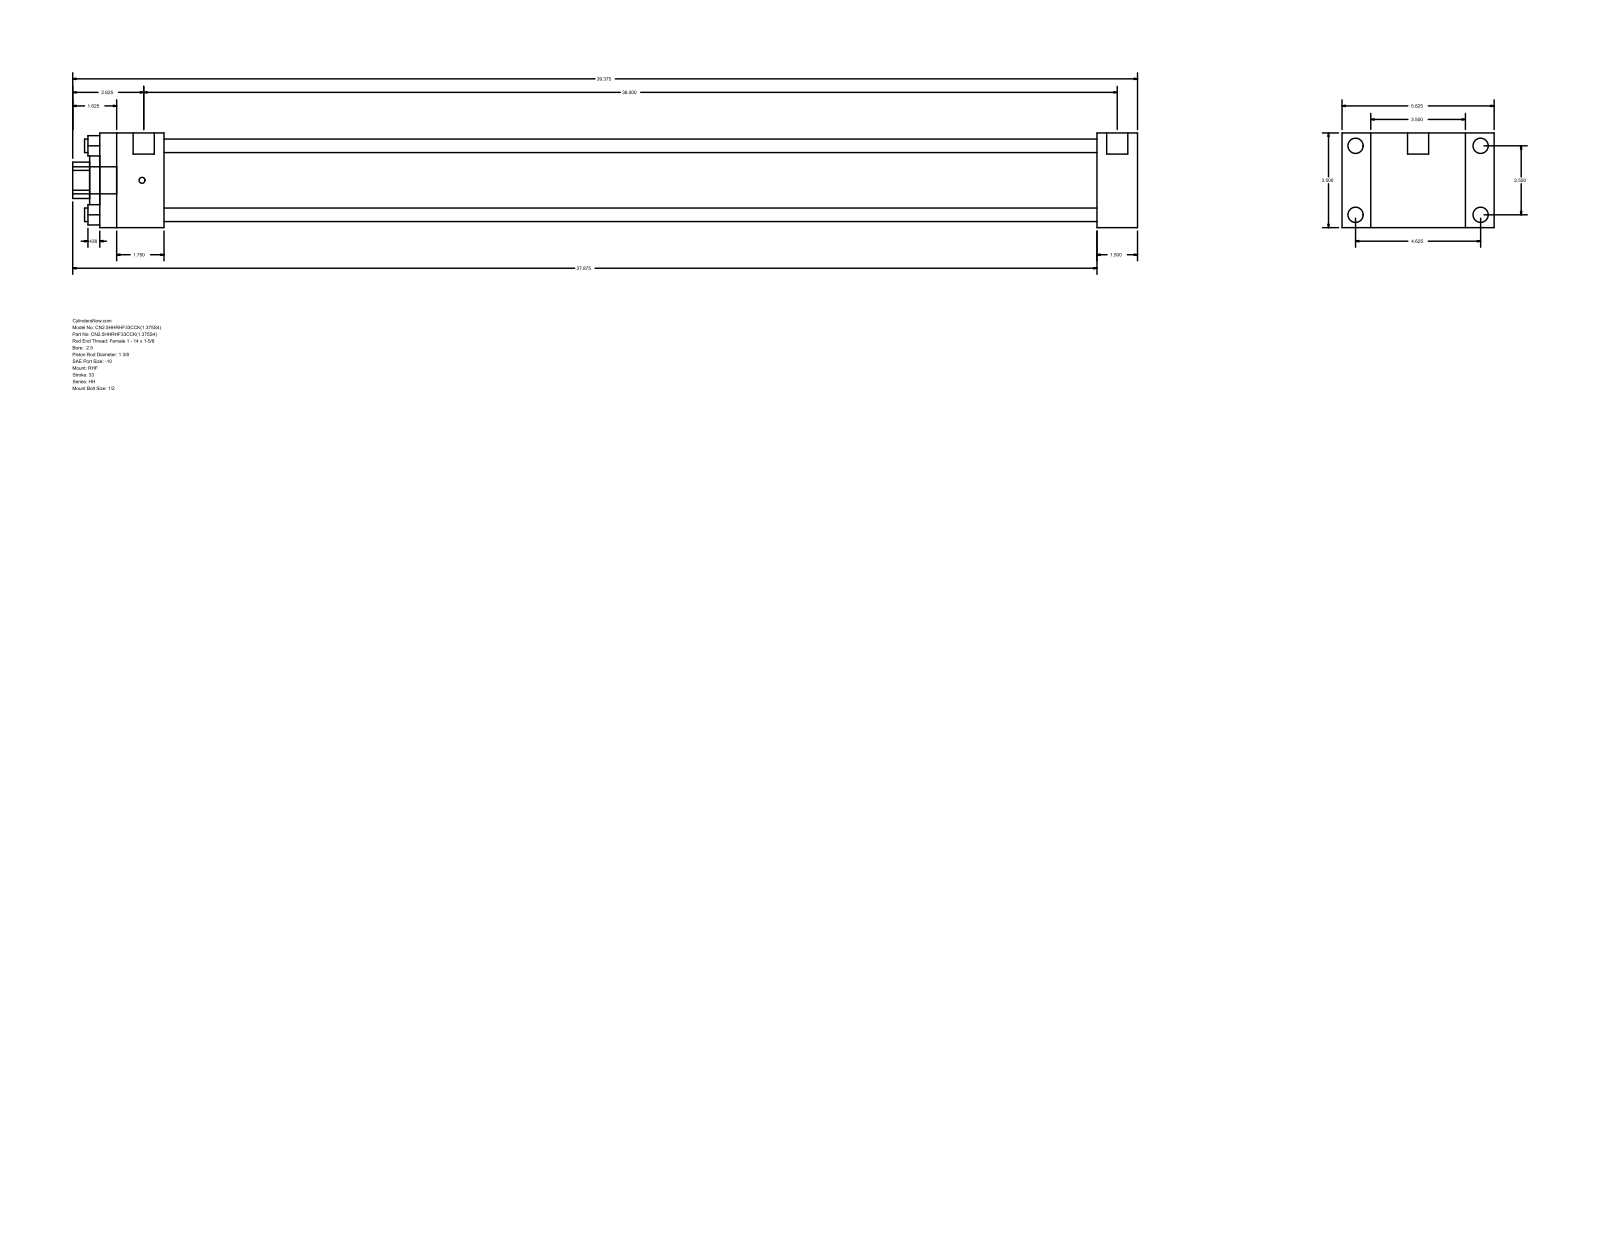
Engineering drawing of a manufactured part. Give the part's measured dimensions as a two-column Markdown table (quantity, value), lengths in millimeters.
| quantity | value |
| --- | --- |
| part name | HH_RHF__0250_1.375 |
| STEP written by | GSSL Pune (CONFIG_CONTROL_DESIGN) |
| units | millimeters |
| bodies | 0 solids, 88 faces (60 planar, 28 cylindrical, 0 other) |
| overall size | 1000.12 × 142.88 × 88.9 |
| round holes (diameter × count) | 12.7 × 4, 34.92 × 1, 50.8 × 1, 73.03 × 1 |
| round bosses / shafts (diameter × count) | 14.3 × 4, 5.56 × 4, 19.84 × 2, 25.4 × 1 |
| partial cylindrical surfaces (radius × count) | 17.06 × 1 |
| main face-to-face distances | 88.9, 38.1, 26.99, 115.89, 936.62, 974.72, 142.88, 60.32, 876.3, 914.4 |
| hole center spacings | 45.79, 64.76, 91.58 |
